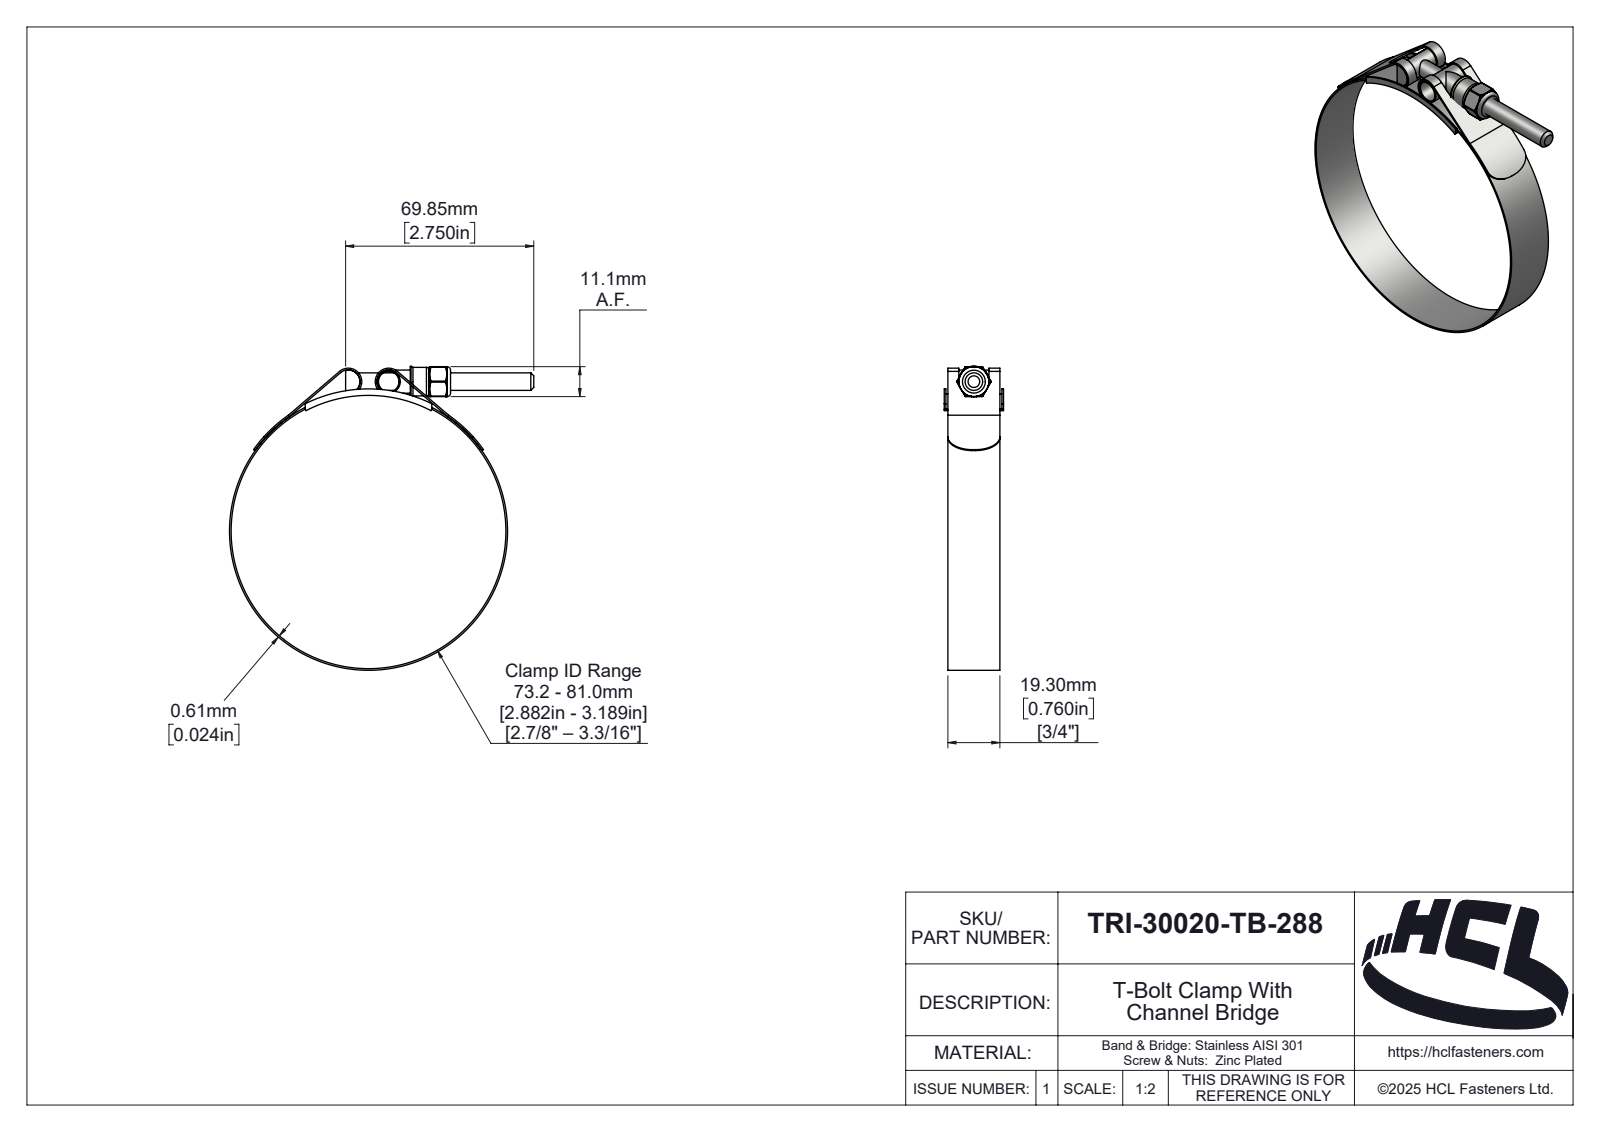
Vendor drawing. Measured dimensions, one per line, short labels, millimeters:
name: TRI-30020-TB-288
written by: SolidWorks 2025 (AUTOMOTIVE_DESIGN)
unit: mm
bodies: 6 solids, 330 faces (44 planar, 122 cylindrical, 164 other)
size: 112.96 × 112.83 × 22
volume: 9 620 mm³; area: 22 870 mm²
holes: 1× ⌀5.4, 1× ⌀6.35, 1× ⌀6.5, 1× ⌀7.58, 1× ⌀102
bosses: 2× ⌀8.58, 1× ⌀103.22, 1× ⌀10.58
rounds: 6× R0.39, 2× R0.5, 2× R4.39, 2× R5, 1× R0.59, 1× R2.42, 1× R3.03, 1× R3.19
face distances: 0.61, 19.3, 1.35, 20.65, 0.74, 21.39, 20.04, 22, 11.11, 20.78
hole spacings: 56
